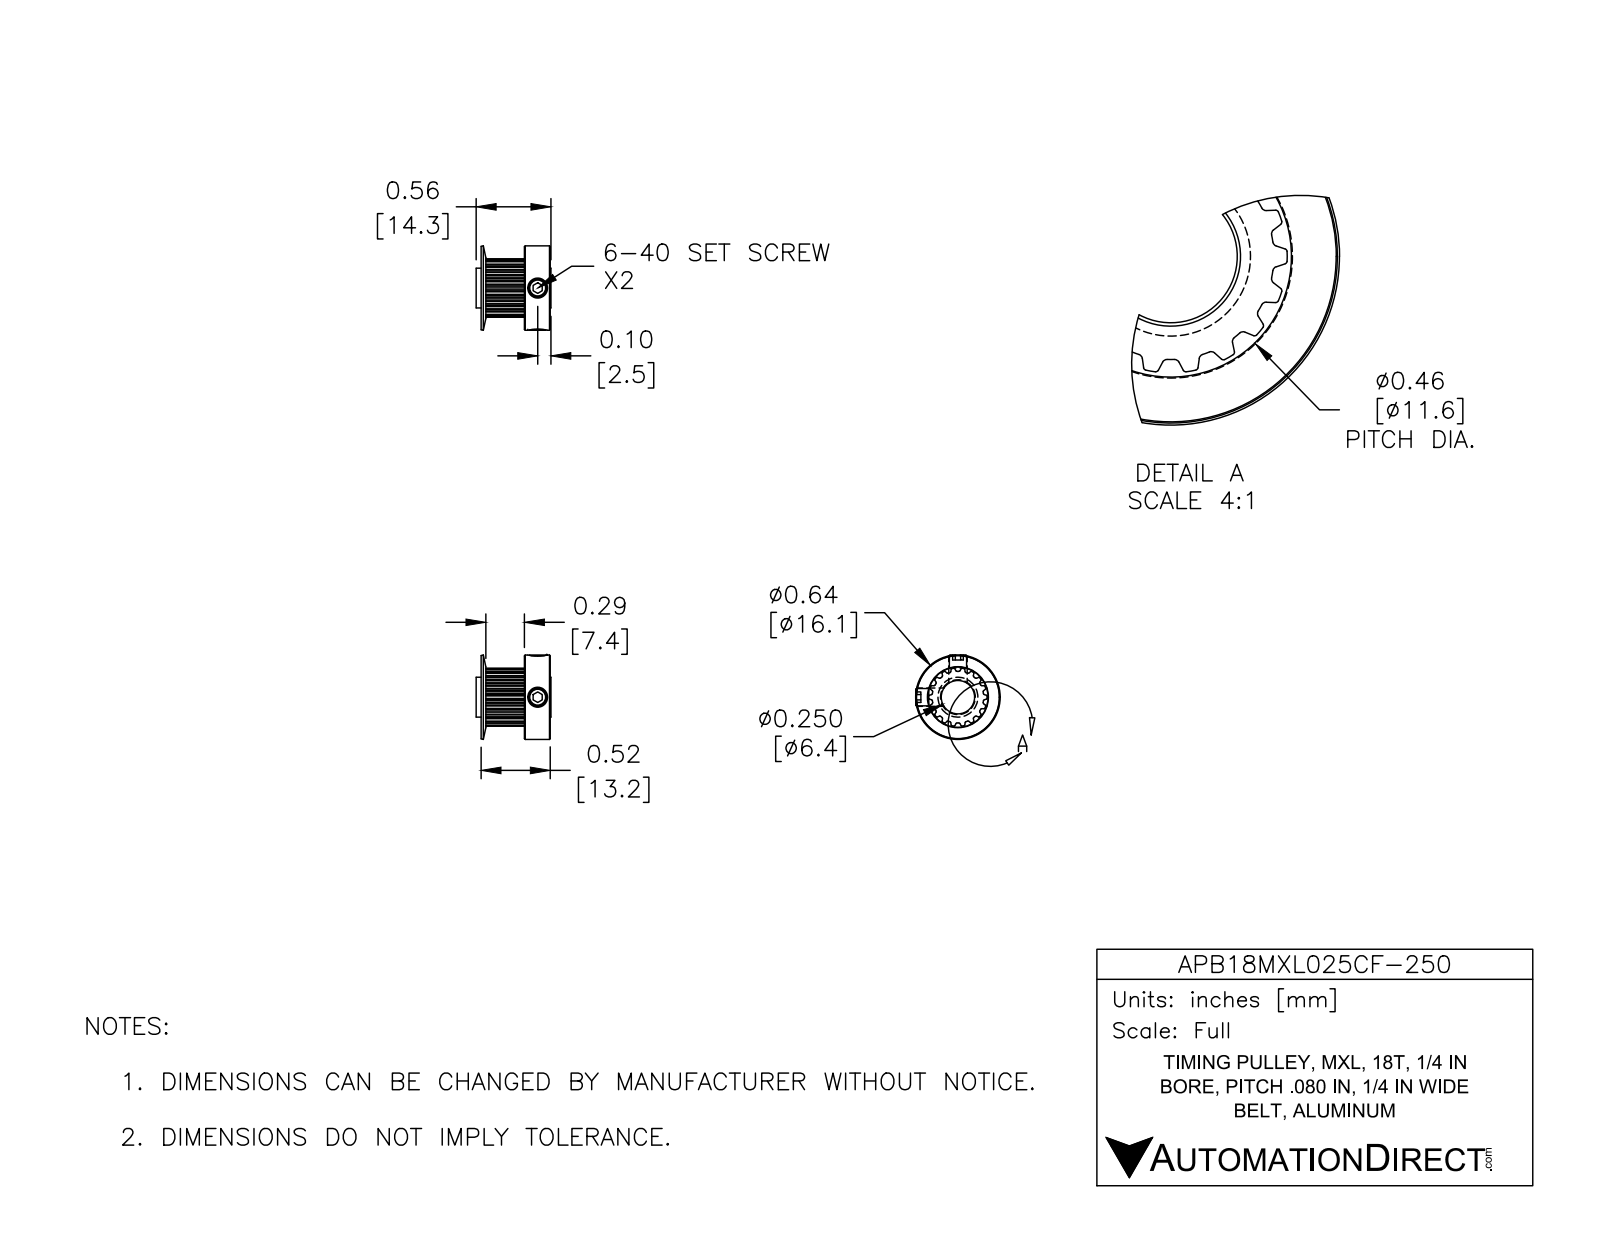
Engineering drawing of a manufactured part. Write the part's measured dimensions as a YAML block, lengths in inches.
part_name: "APB18MXL025CF-250"
step_written_by: "SolidWorks 2016 (AUTOMOTIVE_DESIGN)"
units: inches
bodies: {solids: 3, faces: 219, planar: 60, cylindrical: 137, other: 22}
overall_size: [0.635, 0.635, 0.563]
volume: 0.079
surface_area: 2.583
round_holes:
  - {diameter: 0.138, count: 2}
  - {diameter: 0.25, count: 1}
round_bosses_or_shafts:
  - {diameter: 0.13, count: 2}
  - {diameter: 0.635, count: 1}
  - {diameter: 0.3, count: 1}
partial_cylinders:
  - {radius: 0.005, count: 36}
  - {radius: 0.009, count: 36}
  - {radius: 0.194, count: 1}
  - {radius: 0.219, count: 1}
face_to_face_distances: [0.194, 0.16, 0.309, 0.504, 0.019, 0.29, 0.485, 0.508, 0.489, 0.199]
